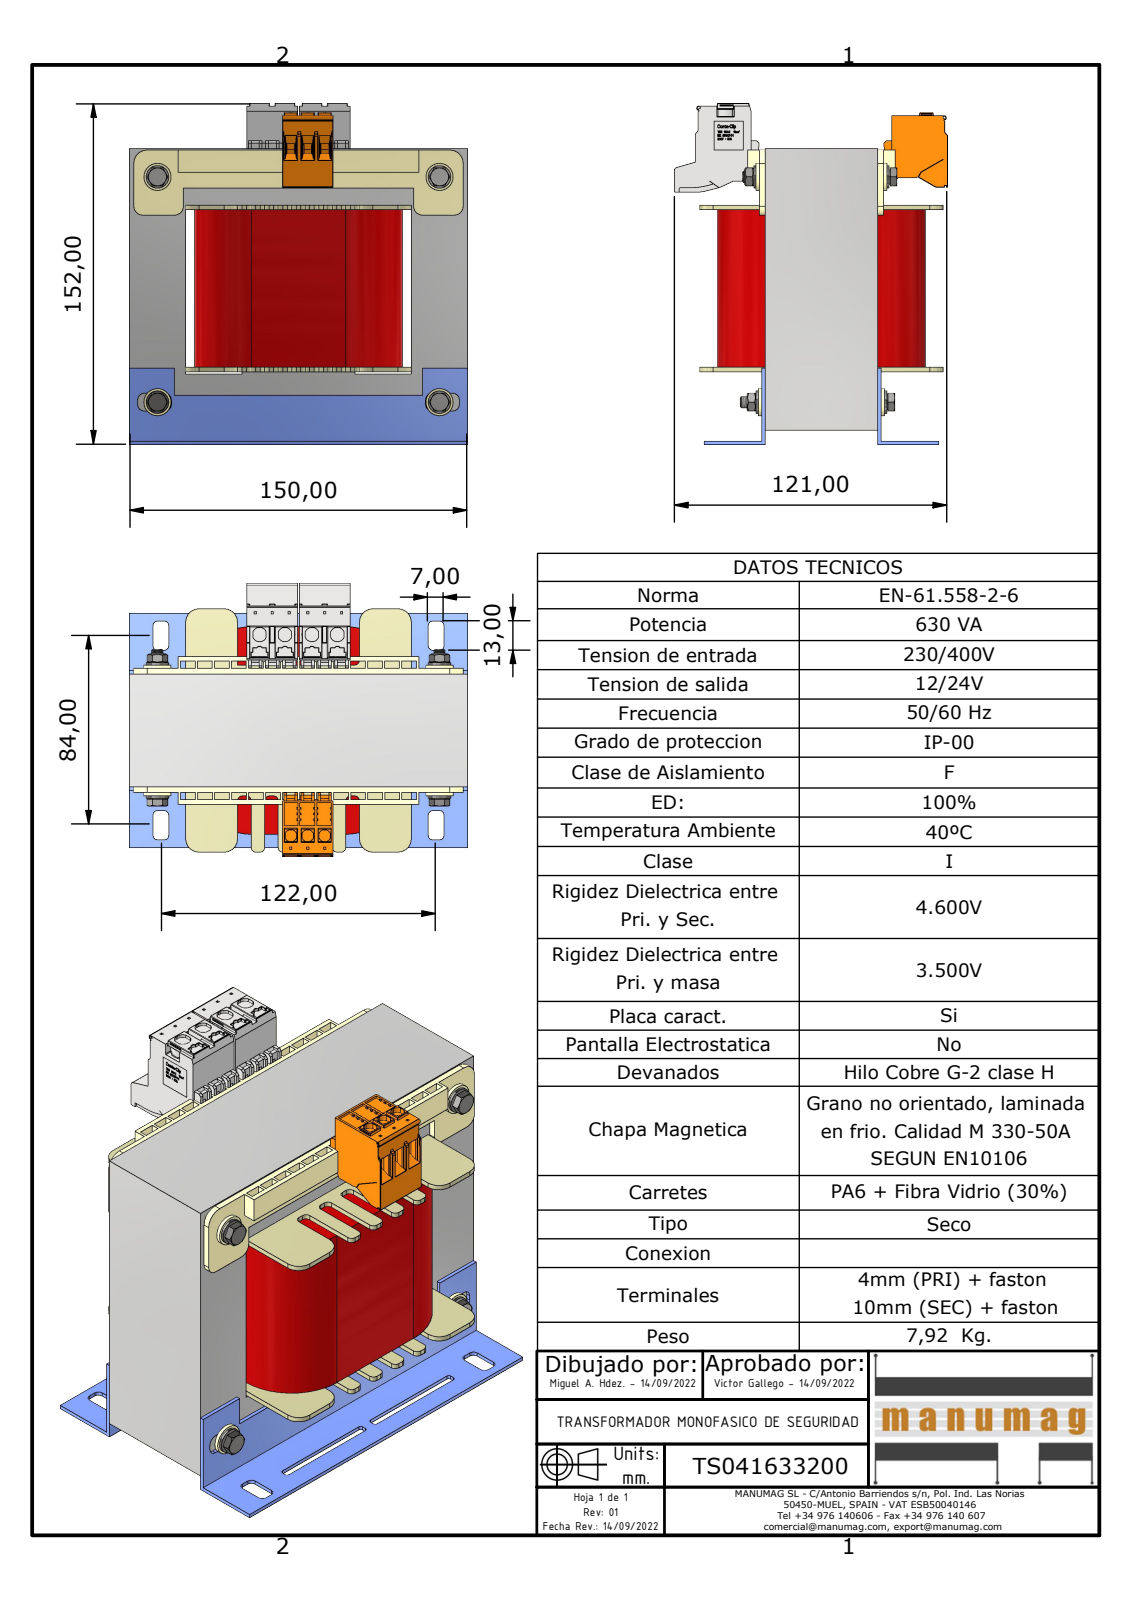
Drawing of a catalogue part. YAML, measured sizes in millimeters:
part_name: "TS041633200; EI150 x 125 - 50 (RC50); AF50DIN; EI 150 X 125 - 50 (+7 more)"
step_written_by: "Autodesk Inventor 2023 (AUTOMOTIVE_DESIGN)"
units: millimeters
bodies: {solids: 33, faces: 6444, planar: 5202, cylindrical: 879, other: 363}
overall_size: [151.6, 150, 121.2]
volume: 1240000
surface_area: 234675
round_holes:
  - {diameter: 4.13, count: 4}
  - {diameter: 5, count: 4}
  - {diameter: 5.3, count: 4}
  - {diameter: 8, count: 4}
round_bosses_or_shafts:
  - {diameter: 12, count: 4}
  - {diameter: 10, count: 4}
  - {diameter: 6.7, count: 4}
  - {diameter: 5.9, count: 4}
  - {diameter: 4.57, count: 4}
partial_cylinders:
  - {radius: 0.2, count: 141}
  - {radius: 0.15, count: 137}
  - {radius: 0.3, count: 63}
  - {radius: 2, count: 55}
  - {radius: 0.1, count: 24}
  - {radius: 1, count: 22}
  - {radius: 0.5, count: 20}
  - {radius: 6, count: 10}
face_to_face_distances: [50, 100, 25, 1.5, 125, 21, 71, 75, 2, 1]
hole_center_spacings: [100, 125, 160.08]
